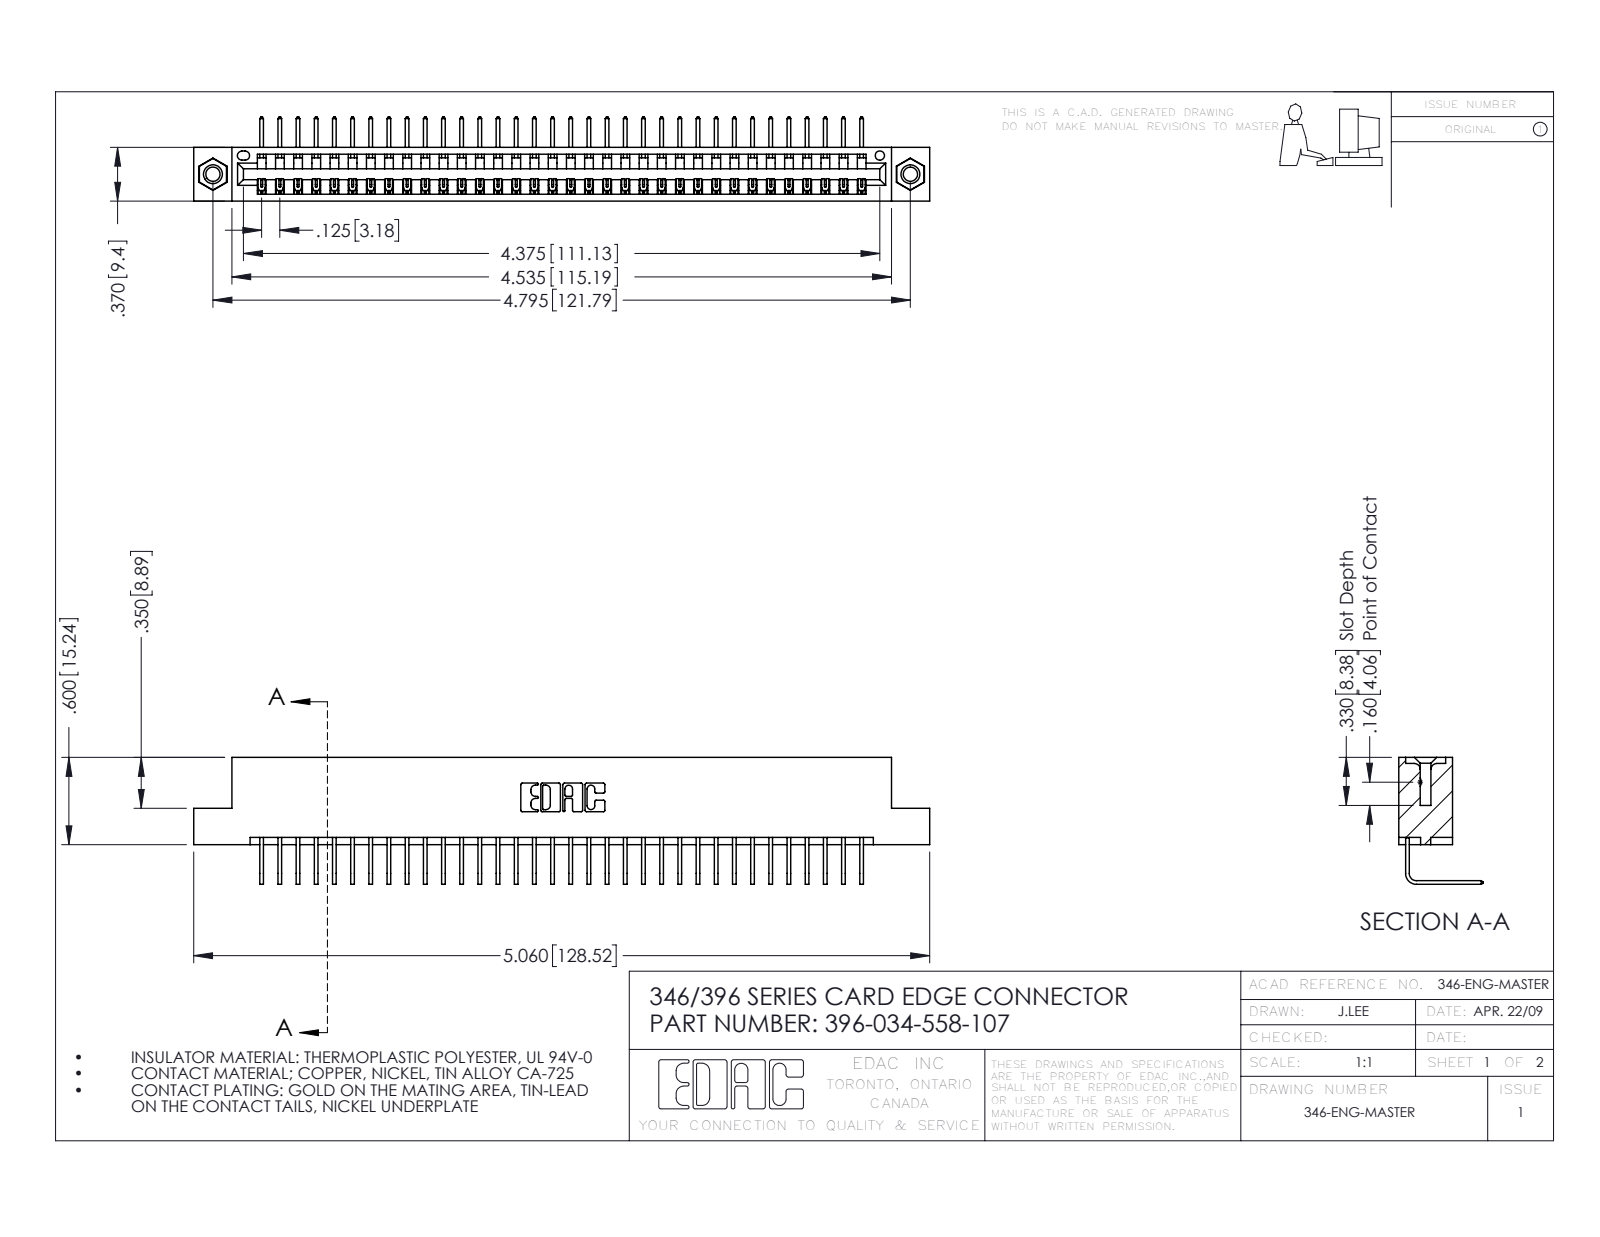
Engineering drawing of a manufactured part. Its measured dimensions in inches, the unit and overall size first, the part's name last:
Units: inches
Overall size (bounding box): 5.06 × 0.873 × 0.58
Round holes (diameter × count): ⌀0.098 ×2, ⌀0.125 ×2, ⌀0.156 ×2, ⌀0.064 ×1
Round bosses / shafts (diameter × count): ⌀0.155 ×2
Partial cylindrical surfaces — rounded edges, fillets, slot ends (radius × count): R0.006 ×68, R0.01 ×22, R0.007 ×6, R0.031 ×6, R0.026 ×3, R0.031 ×2, R0.04 ×2, R0.014 ×1
Main face-to-face distances: 0.322, 0.048, 0.37, 0.25, 0.298, 0.025, 0.072, 0.148, 0.222, 0.1
Hole centre spacings: 0.246, 4.587, 4.795
Volume: 0.753 in³ · Surface area: 24.89 in²
Bodies: 37 solids, 2222 faces (1536 planar, 670 cylindrical, 16 other)
Part name (STEP PRODUCT): 345-292-001_558 Tail - 2; 345-250-001_345-250-005-103; 346 Part_Flush Mounting Lugs - 0.156 Dia-TI; 396-034-558-107
STEP written by: SolidWorks 2016 (CONFIG_CONTROL_DESIGN)
